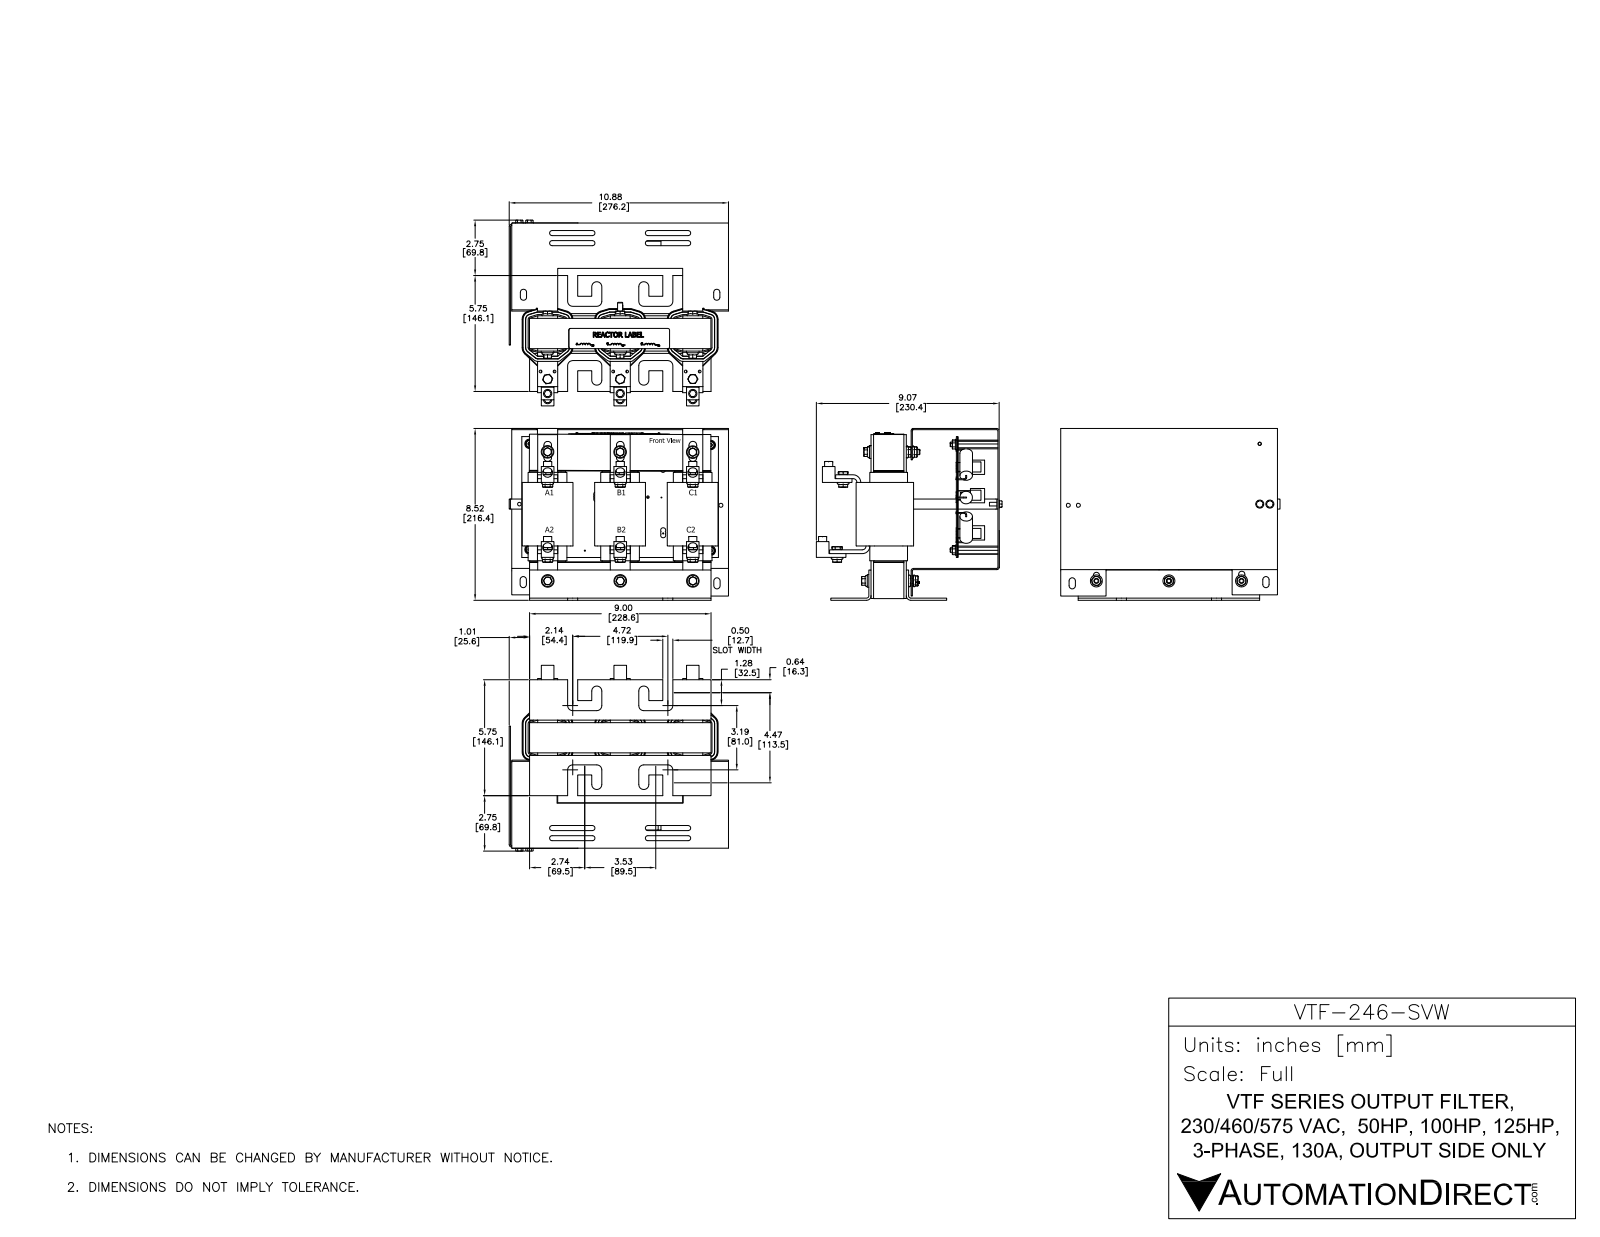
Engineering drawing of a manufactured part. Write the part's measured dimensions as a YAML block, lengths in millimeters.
part_name: "VTF 130A r1"
step_written_by: "SolidWorks 2017 (AUTOMOTIVE_DESIGN)"
units: millimeters
bodies: {solids: 84, faces: 3019, planar: 1507, cylindrical: 835, other: 677}
overall_size: [276.2, 234.1, 216.4]
volume: 2520000
surface_area: 1070000
round_holes:
  - {diameter: 1.5, count: 24}
  - {diameter: 5, count: 12}
  - {diameter: 3.5, count: 9}
  - {diameter: 4.3, count: 6}
  - {diameter: 6.8, count: 6}
  - {diameter: 7.1, count: 6}
  - {diameter: 8.6, count: 6}
  - {diameter: 8.7, count: 6}
  - {diameter: 12.1, count: 6}
  - {diameter: 3.3, count: 4}
  - {diameter: 5.1, count: 4}
  - {diameter: 5.6, count: 4}
round_bosses_or_shafts:
  - {diameter: 6.4, count: 12}
  - {diameter: 0.8, count: 12}
  - {diameter: 1.2, count: 11}
  - {diameter: 15.9, count: 7}
  - {diameter: 10.3, count: 6}
  - {diameter: 10, count: 6}
  - {diameter: 3.2, count: 5}
  - {diameter: 7, count: 3}
partial_cylinders:
  - {radius: 3.2, count: 66}
  - {radius: 0.3, count: 54}
  - {radius: 6.4, count: 24}
  - {radius: 1.5, count: 21}
  - {radius: 4.8, count: 17}
  - {radius: 3.9, count: 16}
  - {radius: 0.8, count: 12}
  - {radius: 2, count: 12}
face_to_face_distances: [1.5, 52.3, 50.8, 176.3, 52, 50.5, 91.4, 53.9, 52.4, 1.8]
hole_center_spacings: [91.4, 182.9, 7.6, 13, 91.8, 9.1, 83.1, 100.8]
